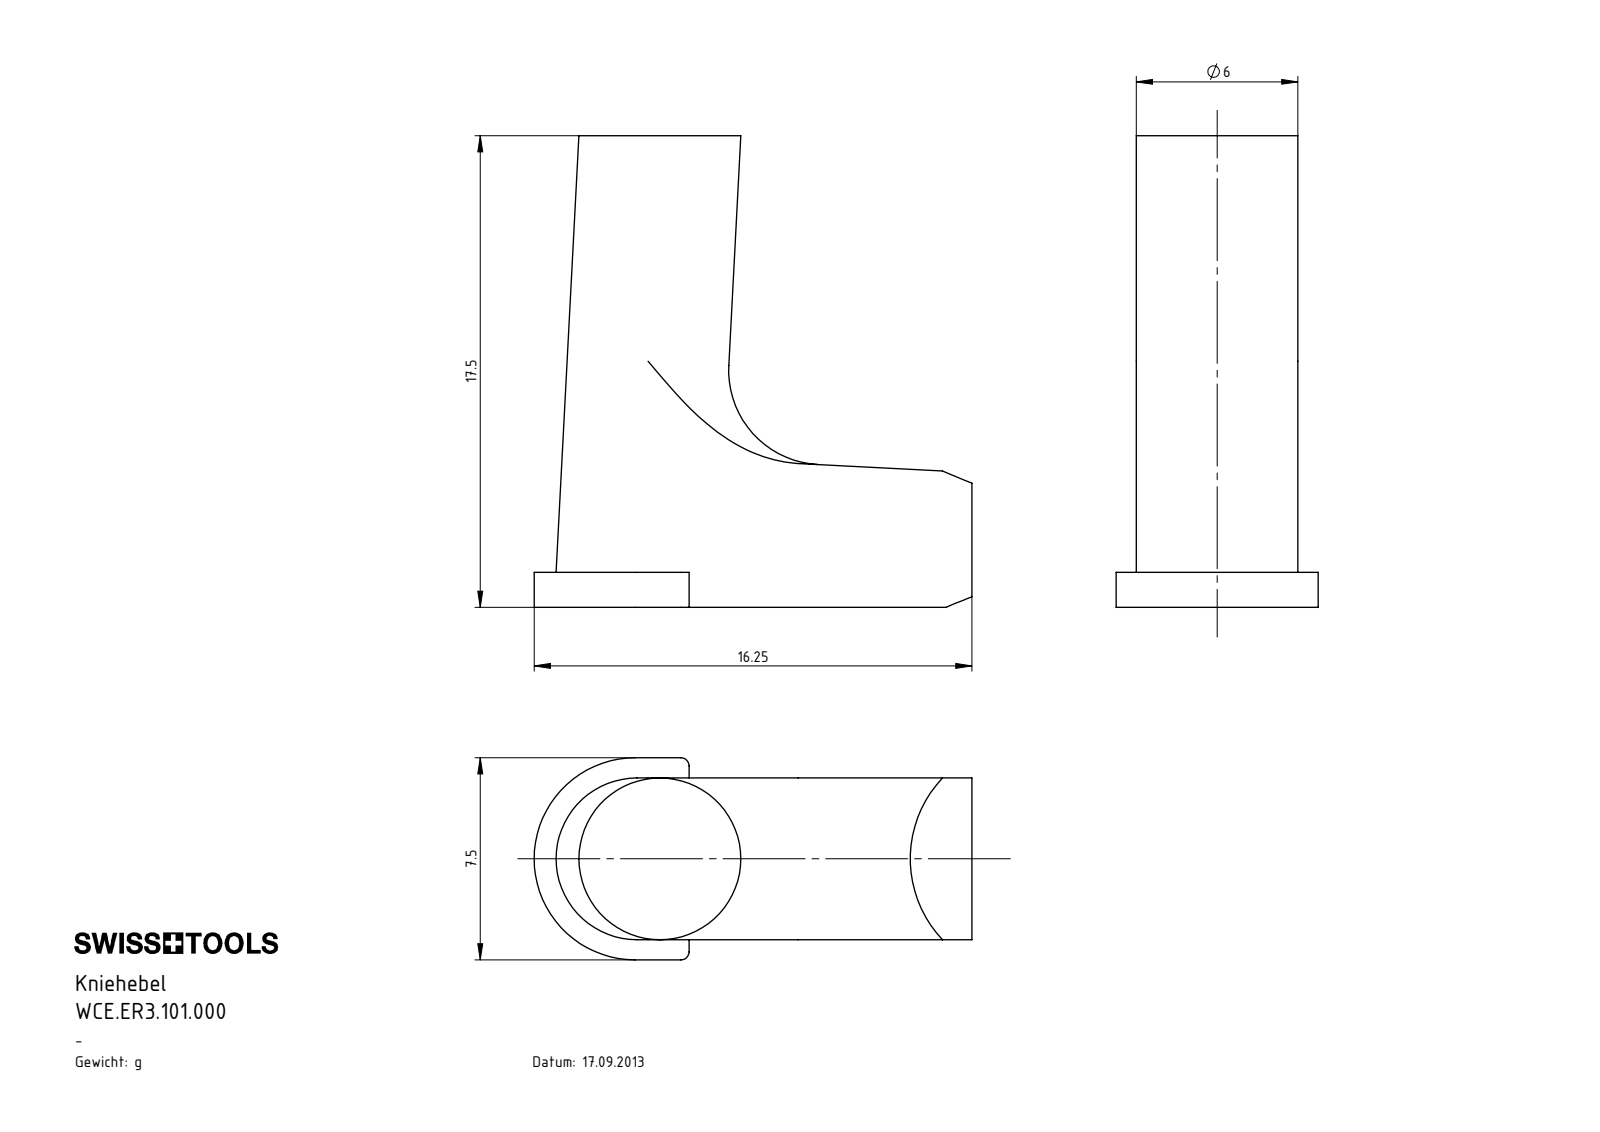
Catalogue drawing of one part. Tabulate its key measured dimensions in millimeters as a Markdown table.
| quantity | value |
| --- | --- |
| part name | WCE.ER3.101.000 |
| STEP written by | SolidWorks 2017 (AUTOMOTIVE_DESIGN) |
| units | millimeters |
| bodies | 1 solid, 18 faces (11 planar, 4 cylindrical, 3 other) |
| overall size | 17.5 × 16.25 × 7.5 |
| volume | 834 mm³ |
| surface area | 631 mm² |
| round bosses / shafts (diameter × count) | 6 × 1 |
| partial cylindrical surfaces (radius × count) | 0.3 × 2, 3.75 × 1 |
| main face-to-face distances | 6, 17.5, 1.3, 16.2, 0.75, 6.75, 7.5, 10.5 |
